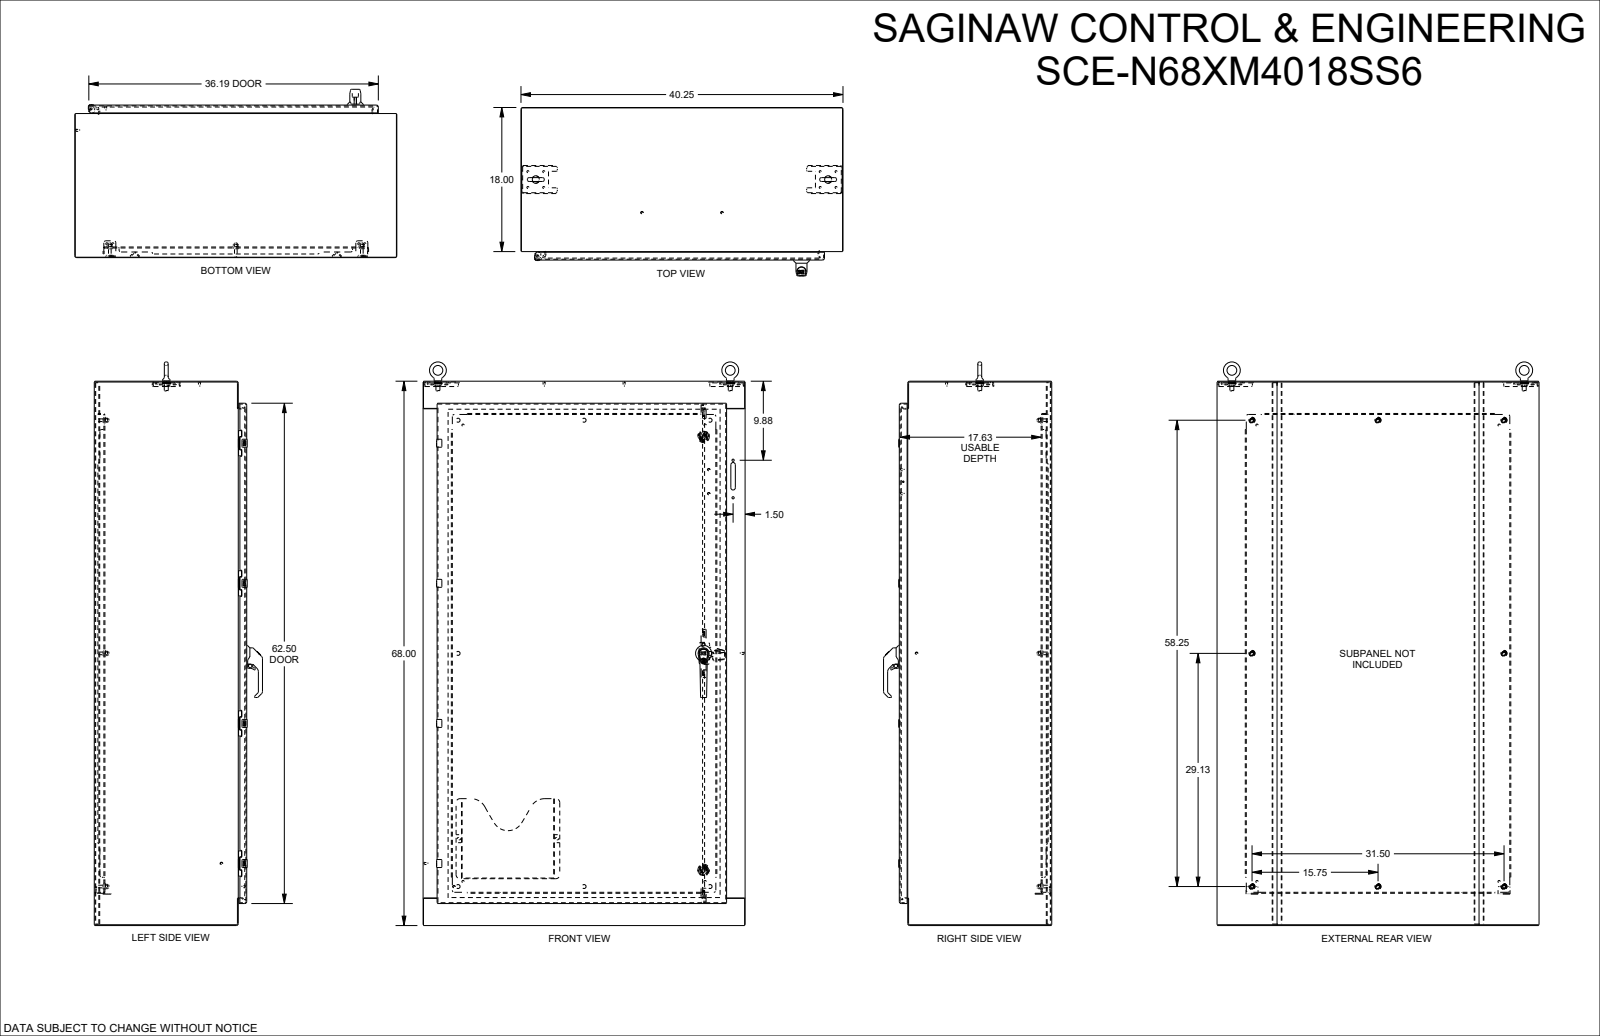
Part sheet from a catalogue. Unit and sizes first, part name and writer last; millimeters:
Units: millimetres
Overall size (bounding box): 1802 × 1022.4 × 534.6
Round holes (diameter × count): ⌀6.4 ×10, ⌀5.2 ×8, ⌀6.2 ×8, ⌀9.5 ×8, ⌀1 ×4, ⌀4.3 ×4, ⌀5.5 ×4, ⌀6.5 ×4, ⌀7.1 ×2, ⌀8.7 ×2, ⌀9.1 ×2, ⌀22.2 ×2
Round bosses / shafts (diameter × count): ⌀4.3 ×12, ⌀6.4 ×8, ⌀6.1 ×8, ⌀5 ×5, ⌀35.6 ×2, ⌀29.8 ×2, ⌀15.2 ×2, ⌀8.7 ×2
Partial cylindrical surfaces — rounded edges, fillets, slot ends (radius × count): R0.8 ×96, R0.4 ×68, R1 ×37, R1.6 ×32, R3.2 ×31, R0.5 ×24, R1 ×22, R2 ×21
Main face-to-face distances: 2.6, 481.4, 2.6, 1019.7, 478.8, 484.1, 1724.6, 454.6, 26.9, 1022.4
Hole centre spacings: 444.5, 889, 12.5, 12.5, 25, 35.5, 35.6, 50.3
Volume: 17 550 000 mm³ · Surface area: 13 210 000 mm²
Bodies: 23 solids, 3153 faces (1334 planar, 1027 cylindrical, 792 other)
Part name (STEP PRODUCT): SCE-N68XM4018
STEP written by: SolidWorks 2023 (AUTOMOTIVE_DESIGN)
